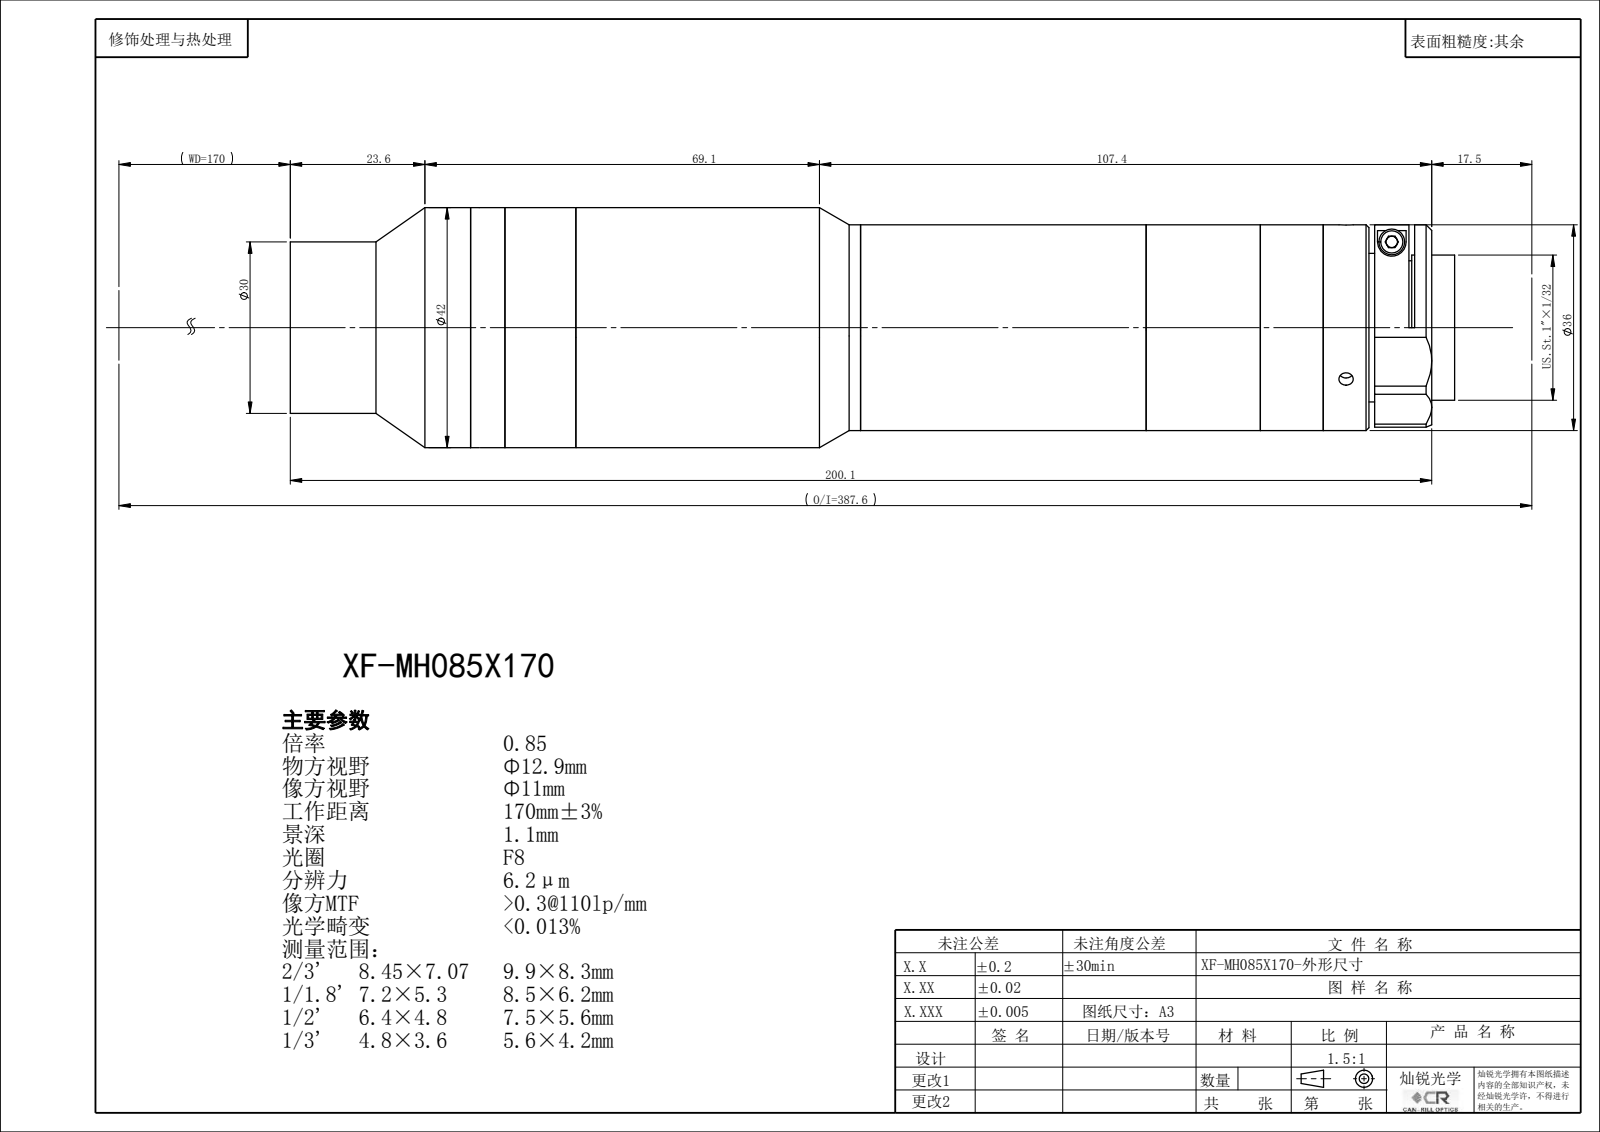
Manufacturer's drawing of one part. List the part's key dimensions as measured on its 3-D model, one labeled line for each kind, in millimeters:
Part name (STEP PRODUCT): XF-MH085X170
STEP written by: SolidWorks 2022 (CONFIG_CONTROL_DESIGN)
Units: millimetres
Bodies: 0 solids, 135 faces (65 planar, 46 cylindrical, 24 other)
Overall size (bounding box): 204.07 × 42 × 42
Round holes (diameter × count): ⌀2.5 ×3, ⌀22.4 ×1, ⌀24 ×1, ⌀26.4 ×1
Round bosses / shafts (diameter × count): ⌀42 ×1, ⌀36 ×1, ⌀34 ×1, ⌀30 ×1, ⌀25.4 ×1
Main face-to-face distances: 50, 20, 99.83, 1.5, 48.74, 50.24, 98.74, 100.24, 70, 28.74
